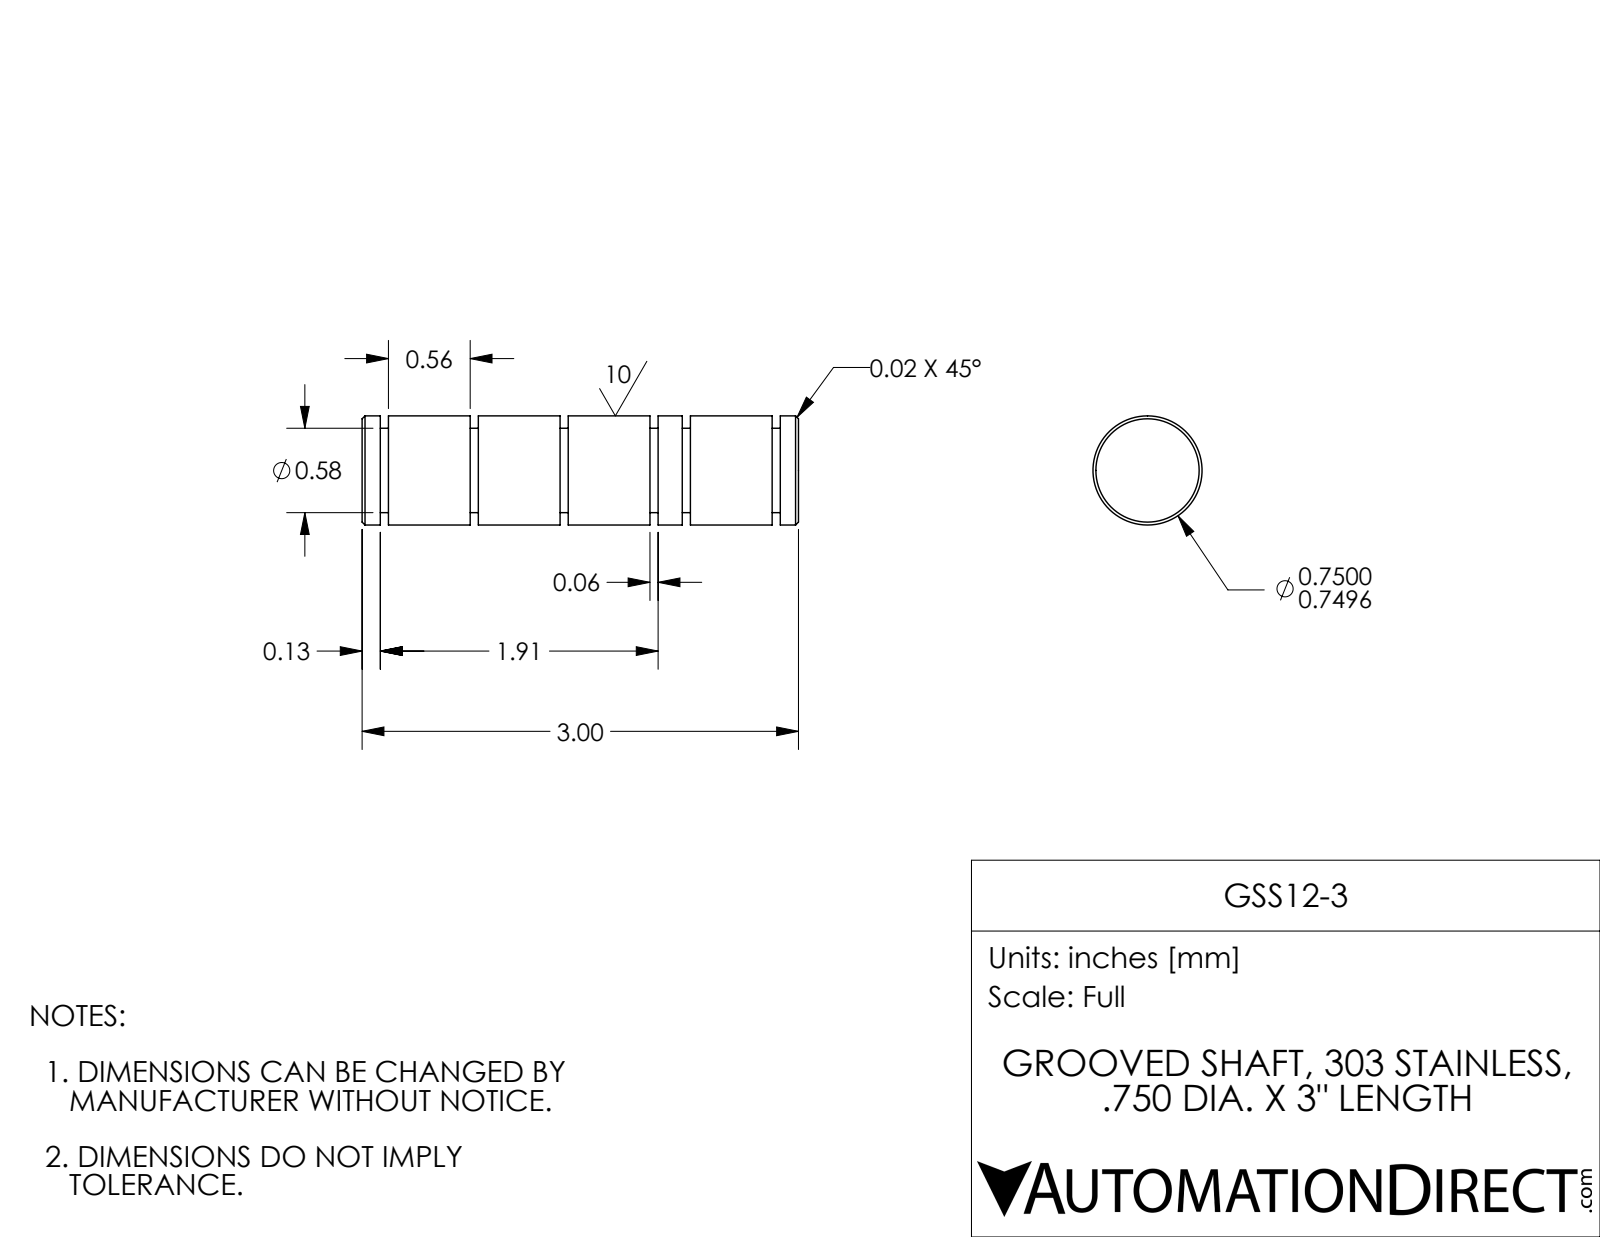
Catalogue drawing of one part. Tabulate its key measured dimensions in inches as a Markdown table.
| quantity | value |
| --- | --- |
| part name | GSS12-3 |
| STEP written by | SolidWorks 2017 (AUTOMOTIVE_DESIGN) |
| units | inches |
| bodies | 1 solid, 44 faces (14 planar, 26 cylindrical, 4 other) |
| overall size | 3 × 0.75 × 0.75 |
| volume | 1.265 in³ |
| surface area | 9.847 in² |
| round bosses / shafts (diameter × count) | 0.75 × 1, 0.58 × 1 |
| main face-to-face distances | 0.618, 0.056, 0.674, 1.236, 0.618, 2.076, 3, 0.181, 0.743, 0.799 |
